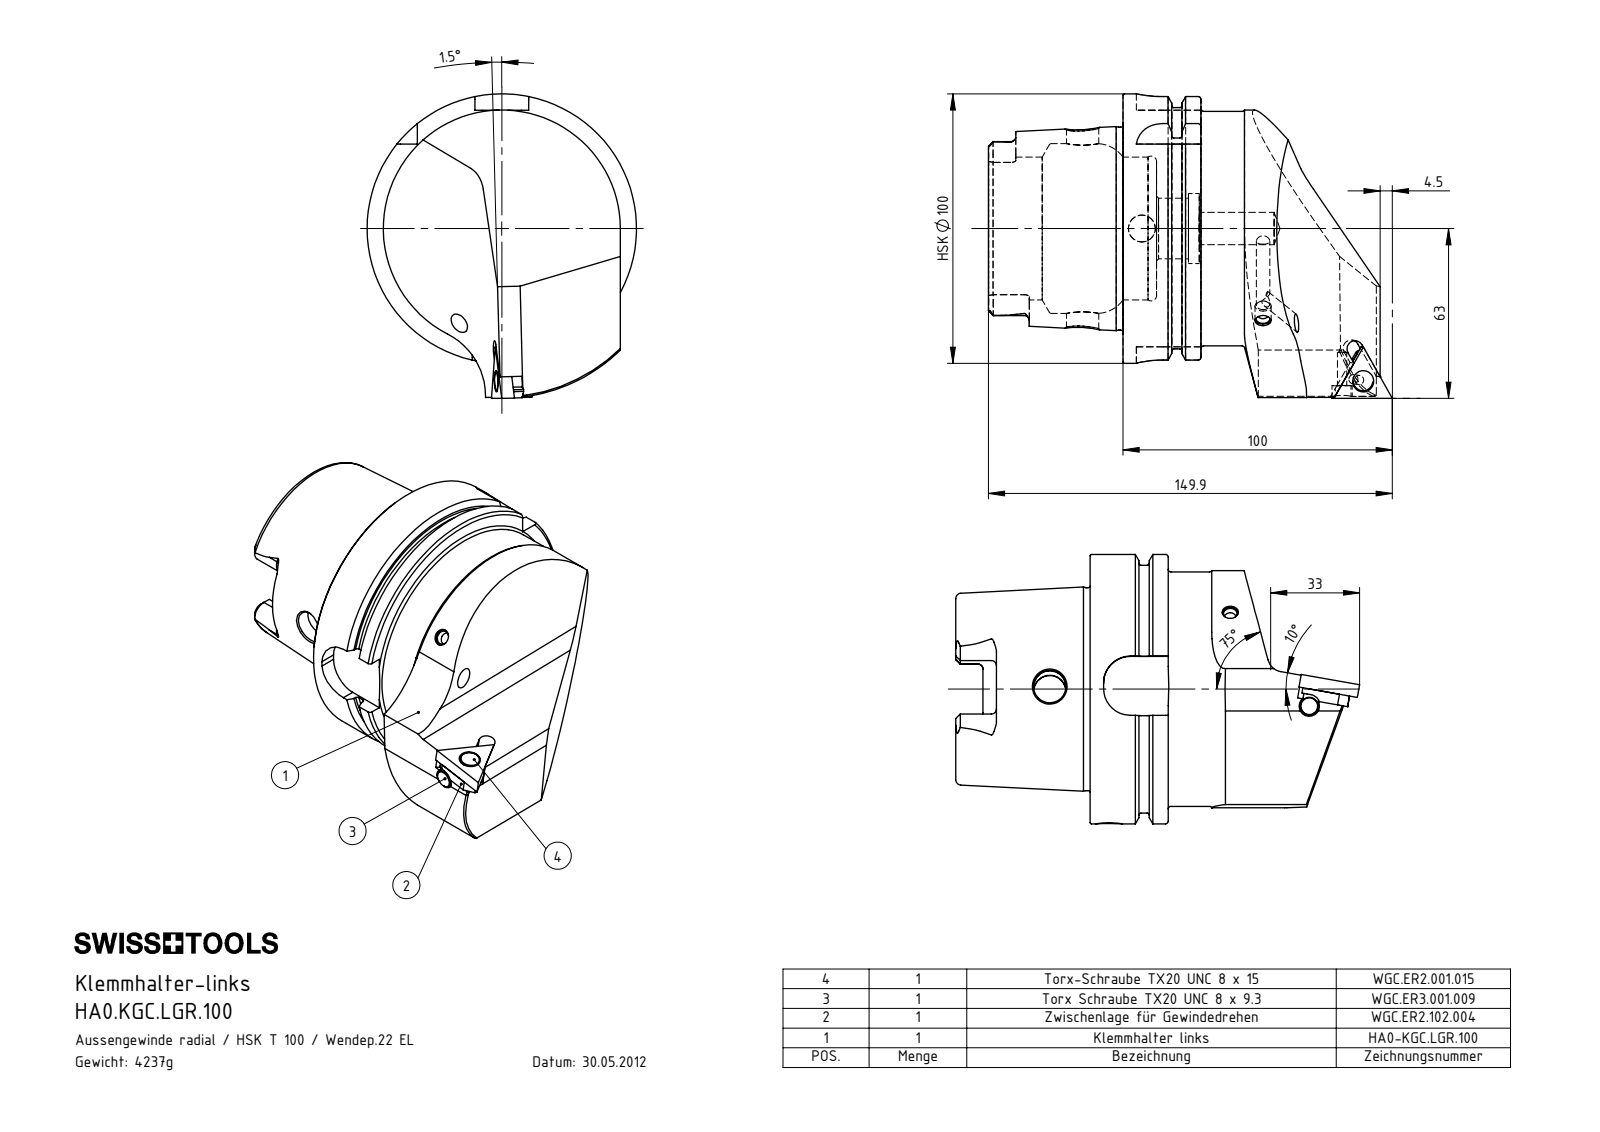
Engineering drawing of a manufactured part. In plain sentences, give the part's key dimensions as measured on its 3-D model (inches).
The part is named "HA0-KGC.LGR.100; Triag S22 T; TRIAG YI22; Triag SU22 T (+3 more)". Its 3-D file was written by "SolidWorks 2015 (CONFIG_CONTROL_DESIGN)". It is 7 solids with 291 faces: 80 planar, 85 cylindrical and 126 other. Overall it measures 5.902 by 4.449 by 3.937 inches. Its volume is 33.02 cubic inches and its surface area 107.7 square inches. Round holes: 2 of diameter 0.136, 2 of diameter 0.197, 2 of diameter 0.472, 1 of diameter 0.192, 1 of diameter 0.209, 1 of diameter 0.394, 1 of diameter 0.886, 1 of diameter 1.024, 1 of diameter 2.087, 1 of diameter 2.48. Round bosses or shafts: 2 of diameter 0.161, 1 of diameter 3.937, 1 of diameter 3.62, 1 of diameter 3.425, 1 of diameter 2.963, 1 of diameter 0.26, 1 of diameter 0.236. Partial cylindrical surfaces (rounded edges, fillets, slot ends): 6 of radius 0.075, 4 of radius 0.192, 4 of radius 0.394, 1 of radius 0.059, 1 of radius 0.079, 1 of radius 0.118, 1 of radius 0.148, 1 of radius 0.157. The main face-to-face distances are 0.49, 1.14, 0.65, 1.965, 2.455, 3.104, 3.457, 3.079, 1.114, 0.624.
